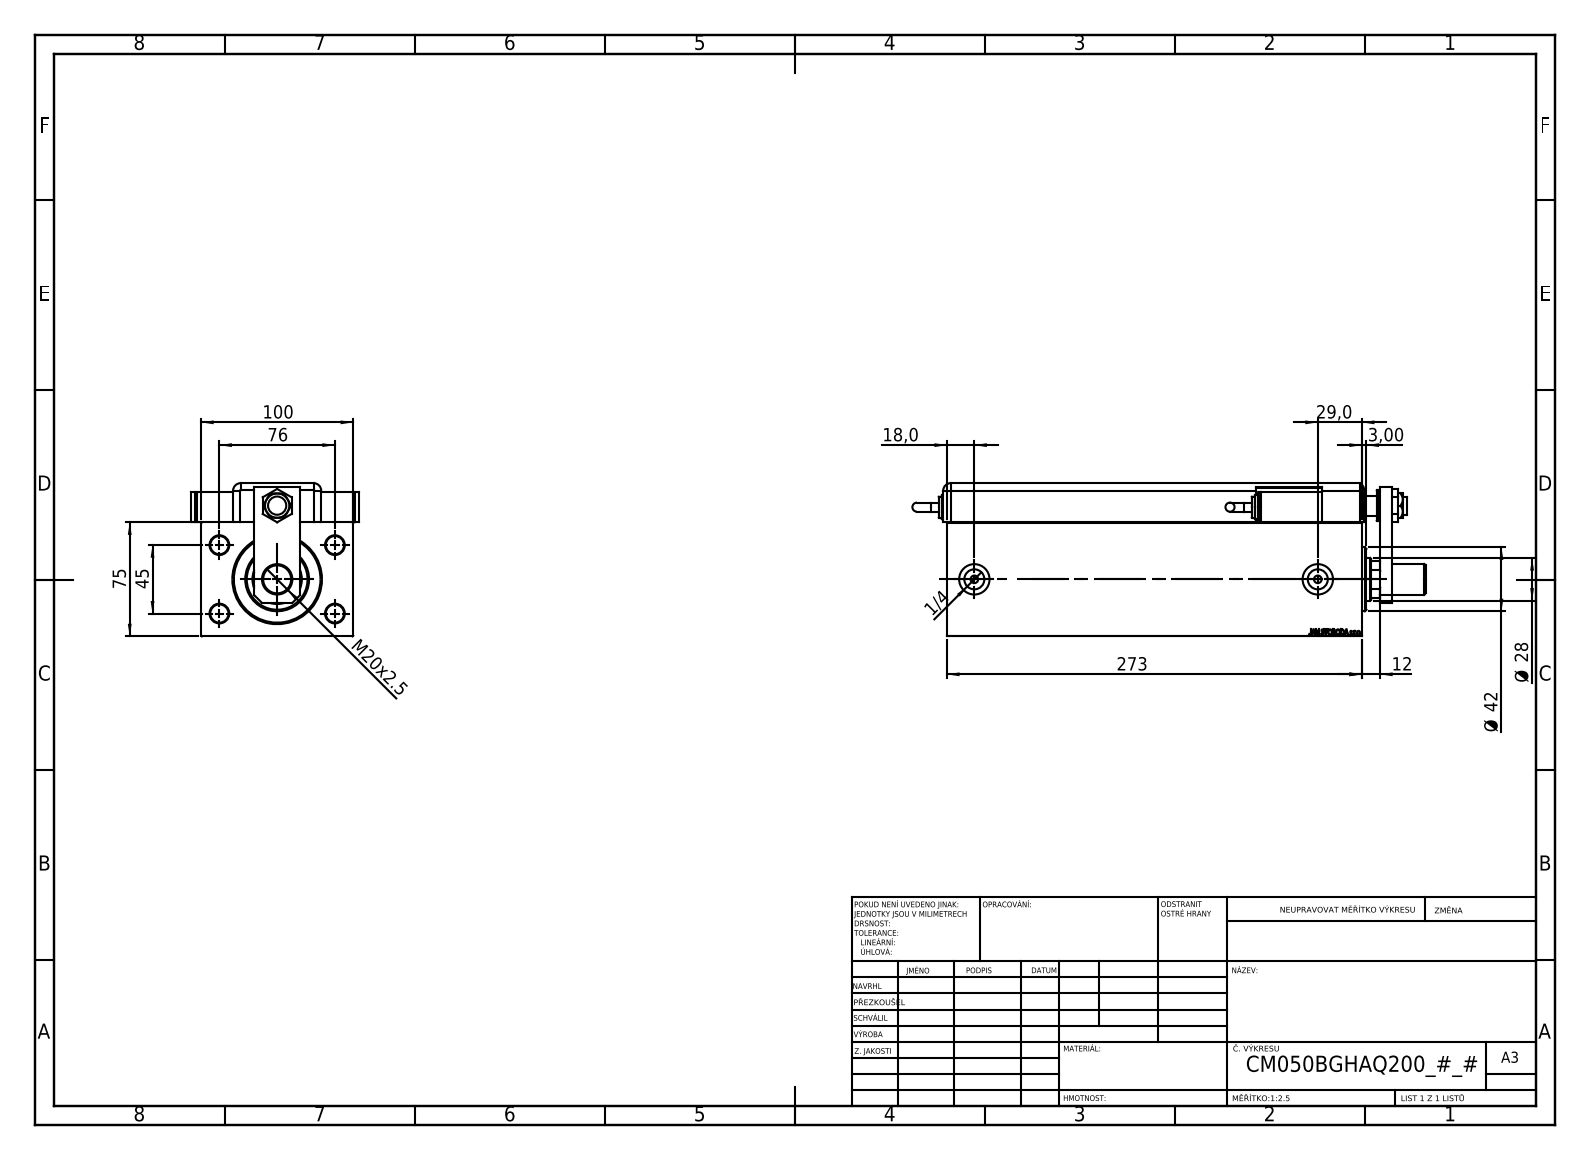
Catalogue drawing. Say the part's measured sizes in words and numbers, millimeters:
The part is named "NUT_D19; V450CM_MALE_METRIC; KRYT; TYC (+7 more)". Its 3-D file was written by "SolidWorks 2019 (CONFIG_CONTROL_DESIGN)". It is 14 solids with 1282 faces: 612 planar, 115 cylindrical and 555 other. Overall it measures 337.76 by 111 by 100.8 millimeters. Its volume is 1 988 000 cubic millimeters and its surface area 299 109 square millimeters. Round holes: 5 of diameter 12, 3 of diameter 20, 2 of diameter 4, 2 of diameter 5, 2 of diameter 8, 2 of diameter 13.16, 1 of diameter 13, 1 of diameter 14, 1 of diameter 18.5, 1 of diameter 28, 1 of diameter 31.5, 1 of diameter 32.5. Round bosses or shafts: 3 of diameter 20, 2 of diameter 16, 2 of diameter 14, 2 of diameter 6, 1 of diameter 42, 1 of diameter 18. Partial cylindrical surfaces (rounded edges, fillets, slot ends): 9 of radius 5, 1 of radius 10, 1 of radius 13.5. The main face-to-face distances are 75, 3, 100, 25.8, 100.8, 97.8, 22.8, 24, 21, 79. The hole center spacings are 44.16, 45, 46.04, 76, 80.53, 88.32, 20, 48.5.
